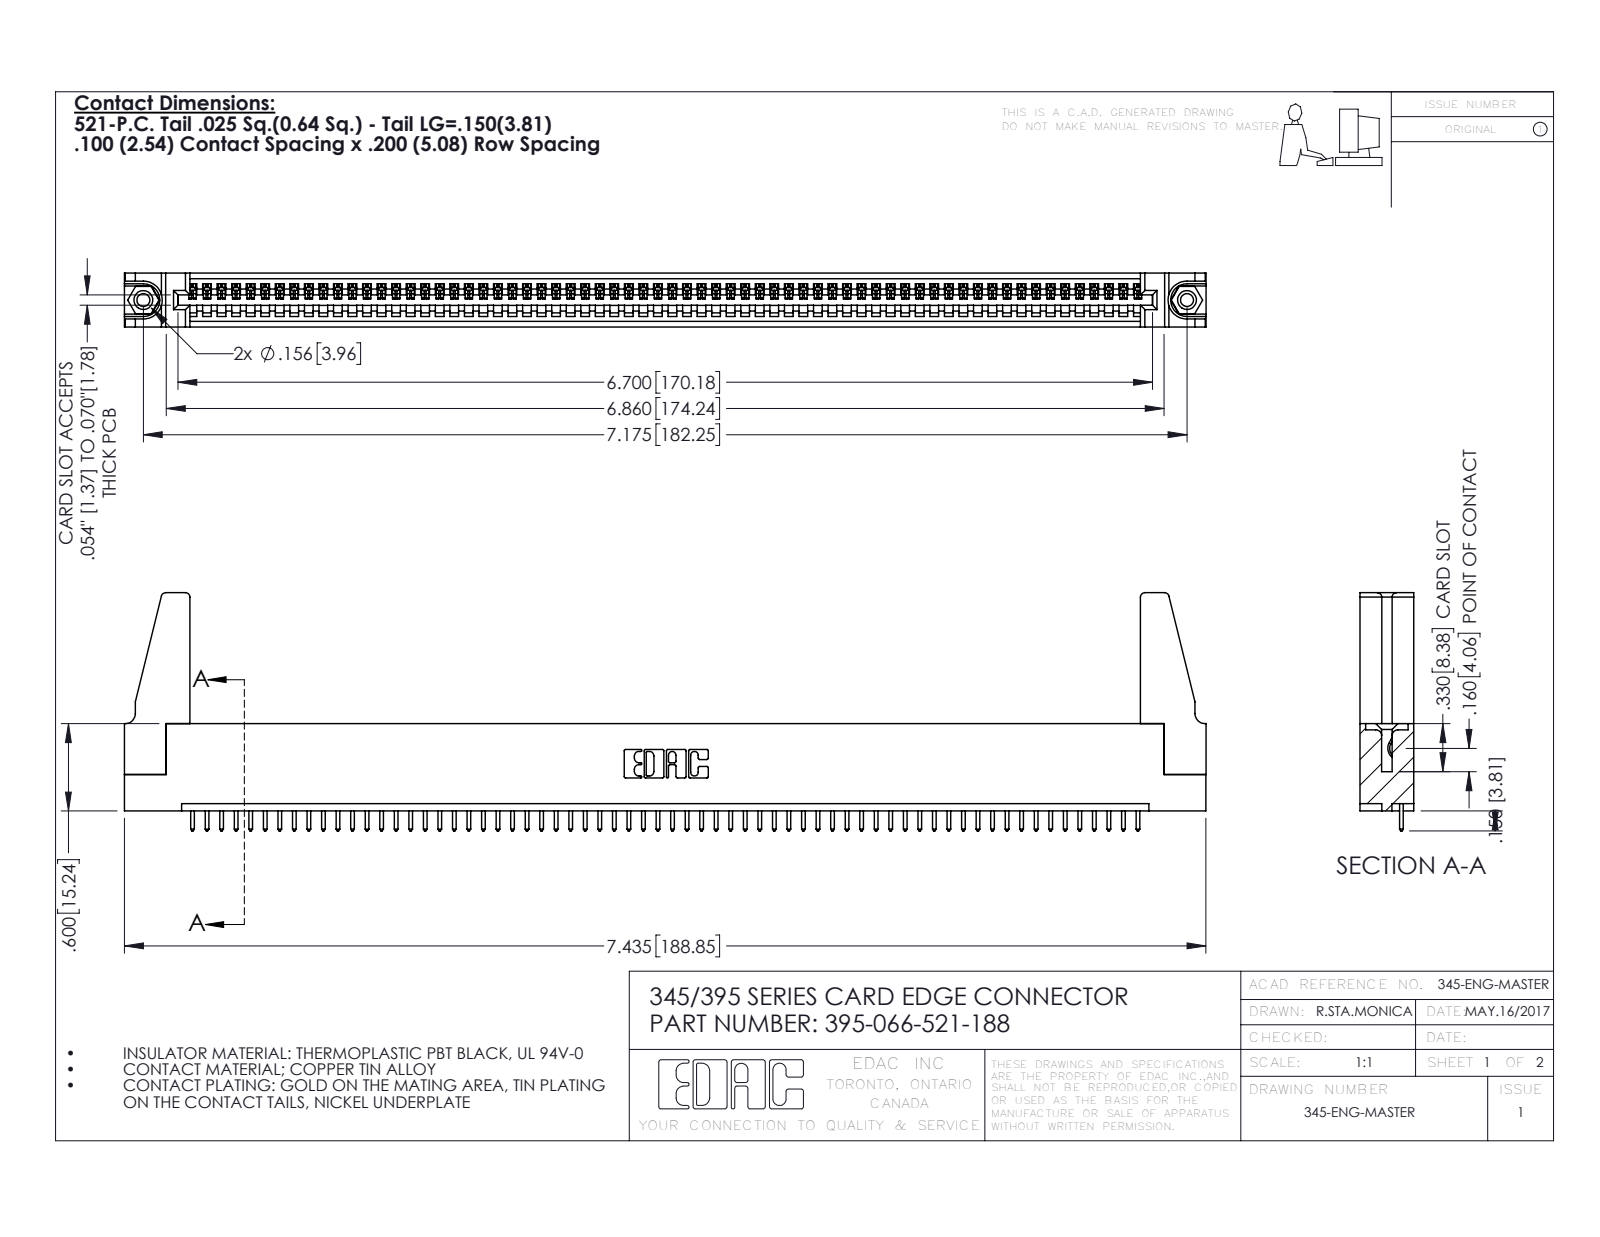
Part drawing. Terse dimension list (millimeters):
name: 395-066-521-188; 345-250-001_345-250-001-102; 345-220-078_345-220-088; 345 Part_Flush Mounting Lugs - 0.156 Dia-TH (+1 more)
written by: SolidWorks 2016 (CONFIG_CONTROL_DESIGN)
unit: mm
bodies: 71 solids, 4078 faces (2792 planar, 1270 cylindrical, 16 other)
size: 188.9 × 41.6 × 9.4
volume: 21 200 mm³; area: 26 570 mm²
holes: 2× ⌀2.3, 2× ⌀3.2, 2× ⌀4, 1× ⌀1.6
bosses: 2× ⌀3.9
rounds: 132× R0.2, 132× R0.3, 22× R0.3, 8× R0.8, 6× R0.2, 6× R0.8, 3× R0.7, 2× R0.8
face distances: 1.8, 7.6, 9.4, 5.1, 2.5, 6.9, 0.6, 5.7, 3.8, 1.8
hole spacings: 6.9, 176.3, 182.2
